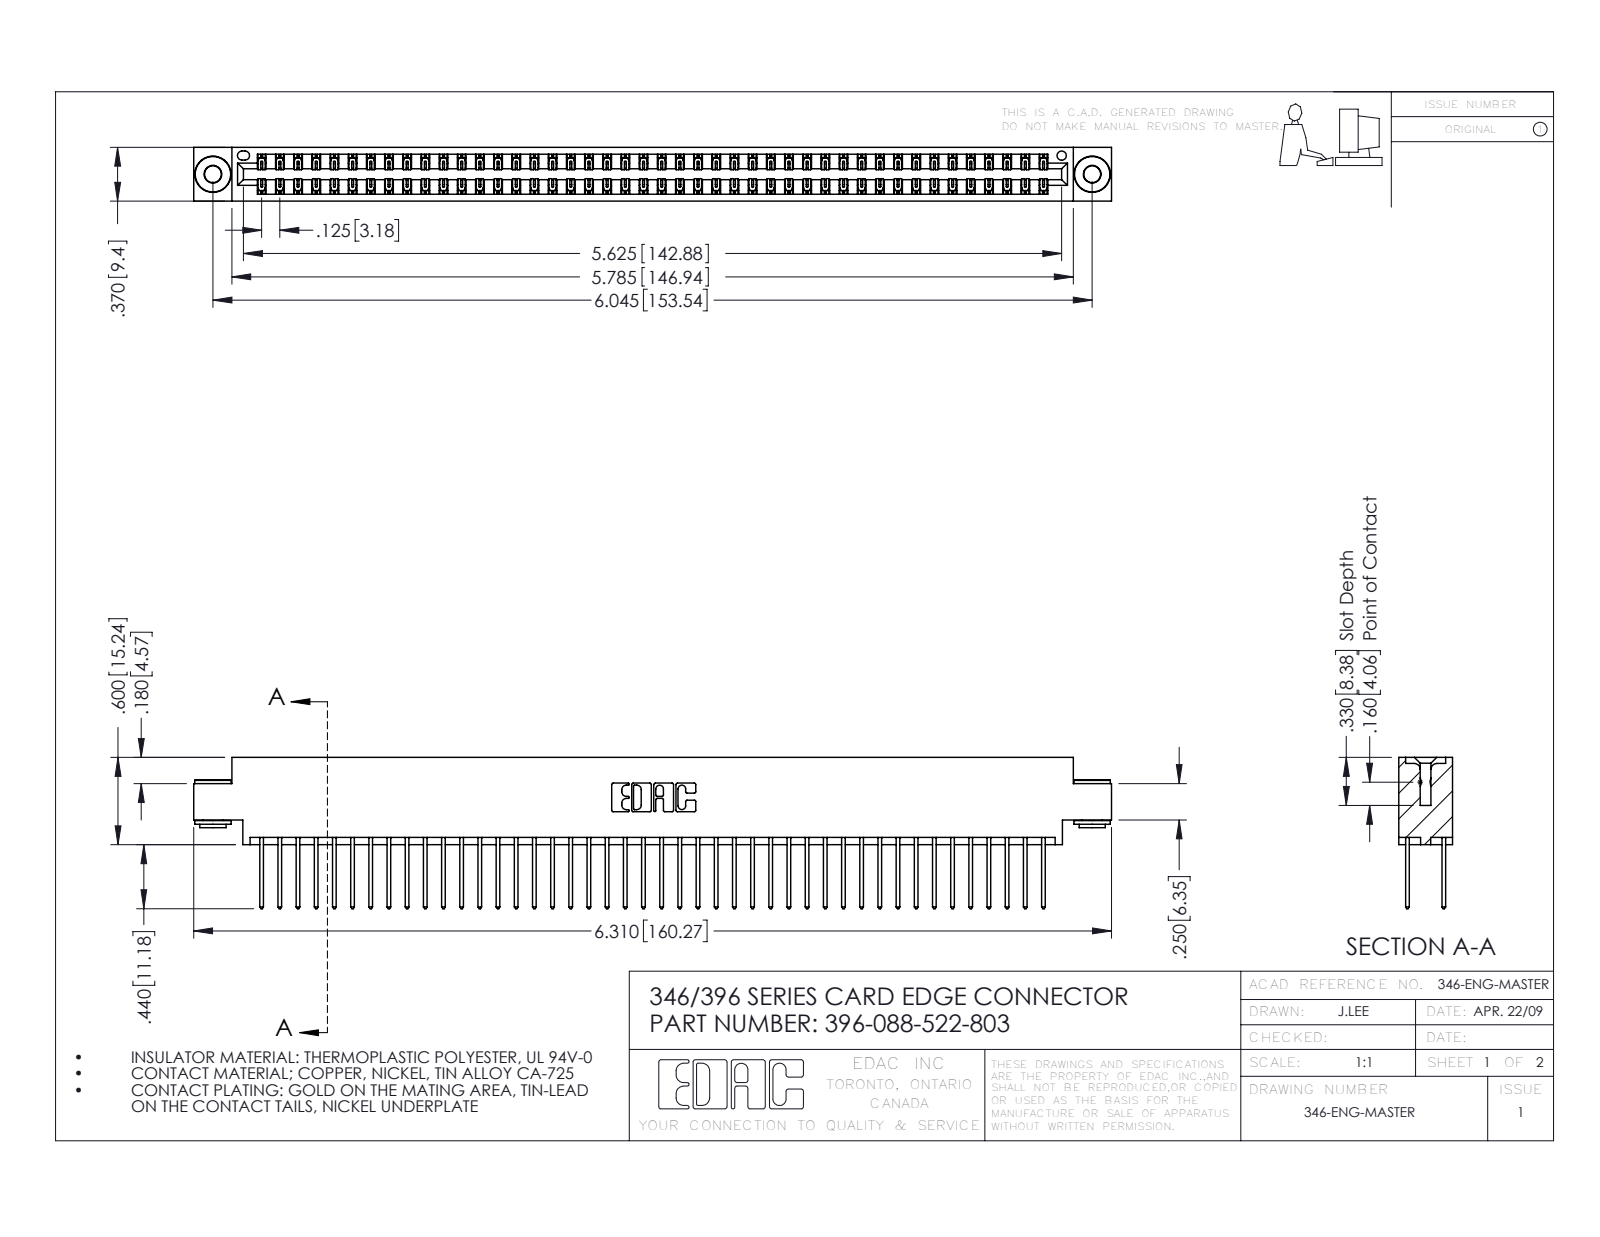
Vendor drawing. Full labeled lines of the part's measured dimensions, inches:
Part name (STEP PRODUCT): 345-250-002_345-250-002-102; 346 Part_0.170 Offset - 0.156 Dia-TH; 396-088-522-803; 345-292-001_345-293-122
STEP written by: SolidWorks 2016 (CONFIG_CONTROL_DESIGN)
Units: inches
Bodies: 91 solids, 4740 faces (3170 planar, 1562 cylindrical, 8 other)
Overall size (bounding box): 6.31 × 1.04 × 0.37
Volume: 0.96 in³ · Surface area: 35.8 in²
Round holes (diameter × count): ⌀0.116 ×2, ⌀0.156 ×2, ⌀0.064 ×1
Round bosses / shafts (diameter × count): ⌀0.25 ×2, ⌀0.18 ×2, ⌀0.136 ×2
Partial cylindrical surfaces — rounded edges, fillets, slot ends (radius × count): R0.006 ×132, R0.01 ×88, R0.01 ×22, R0.007 ×6, R0.031 ×6, R0.026 ×3, R0.014 ×2, R0.022 ×2
Main face-to-face distances: 0.048, 0.322, 0.25, 0.37, 0.025, 0.072, 0.298, 0.275, 0.148, 0.222
Hole centre spacings: 0.246, 5.836, 6.045
